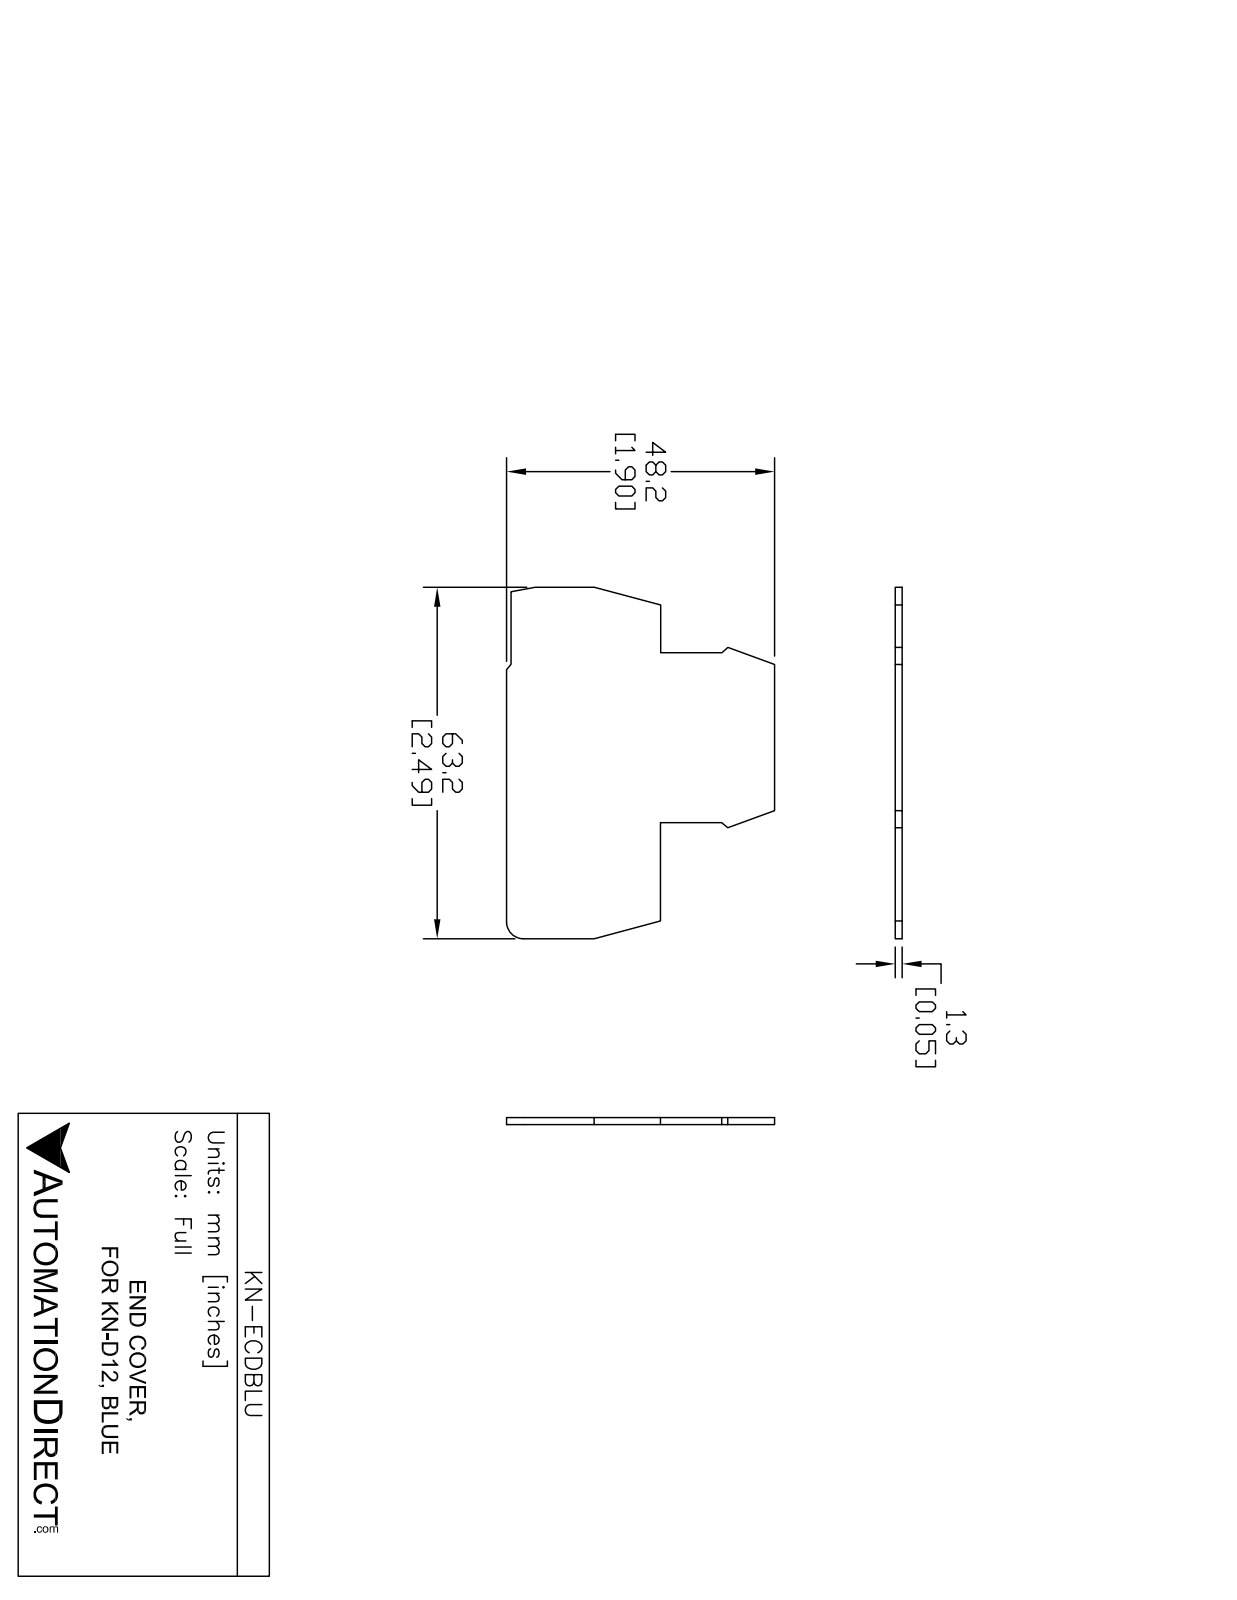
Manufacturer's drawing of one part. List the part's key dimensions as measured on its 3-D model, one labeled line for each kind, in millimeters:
Part name (STEP PRODUCT): KN-ECD
STEP written by: SolidWorks 2014 (AUTOMOTIVE_DESIGN)
Units: millimetres
Bodies: 1 solid, 21 faces (19 planar, 2 cylindrical, 0 other)
Overall size (bounding box): 63.25 × 48.2 × 1.25
Volume: 2 895 mm³ · Surface area: 4 897 mm²
Partial cylindrical surfaces — rounded edges, fillets, slot ends (radius × count): R0.5 ×1, R3 ×1
Main face-to-face distances: 1.24, 48.2, 27.66, 20.54, 0.8, 26.86, 47.4, 51.46, 30.57, 20.89
